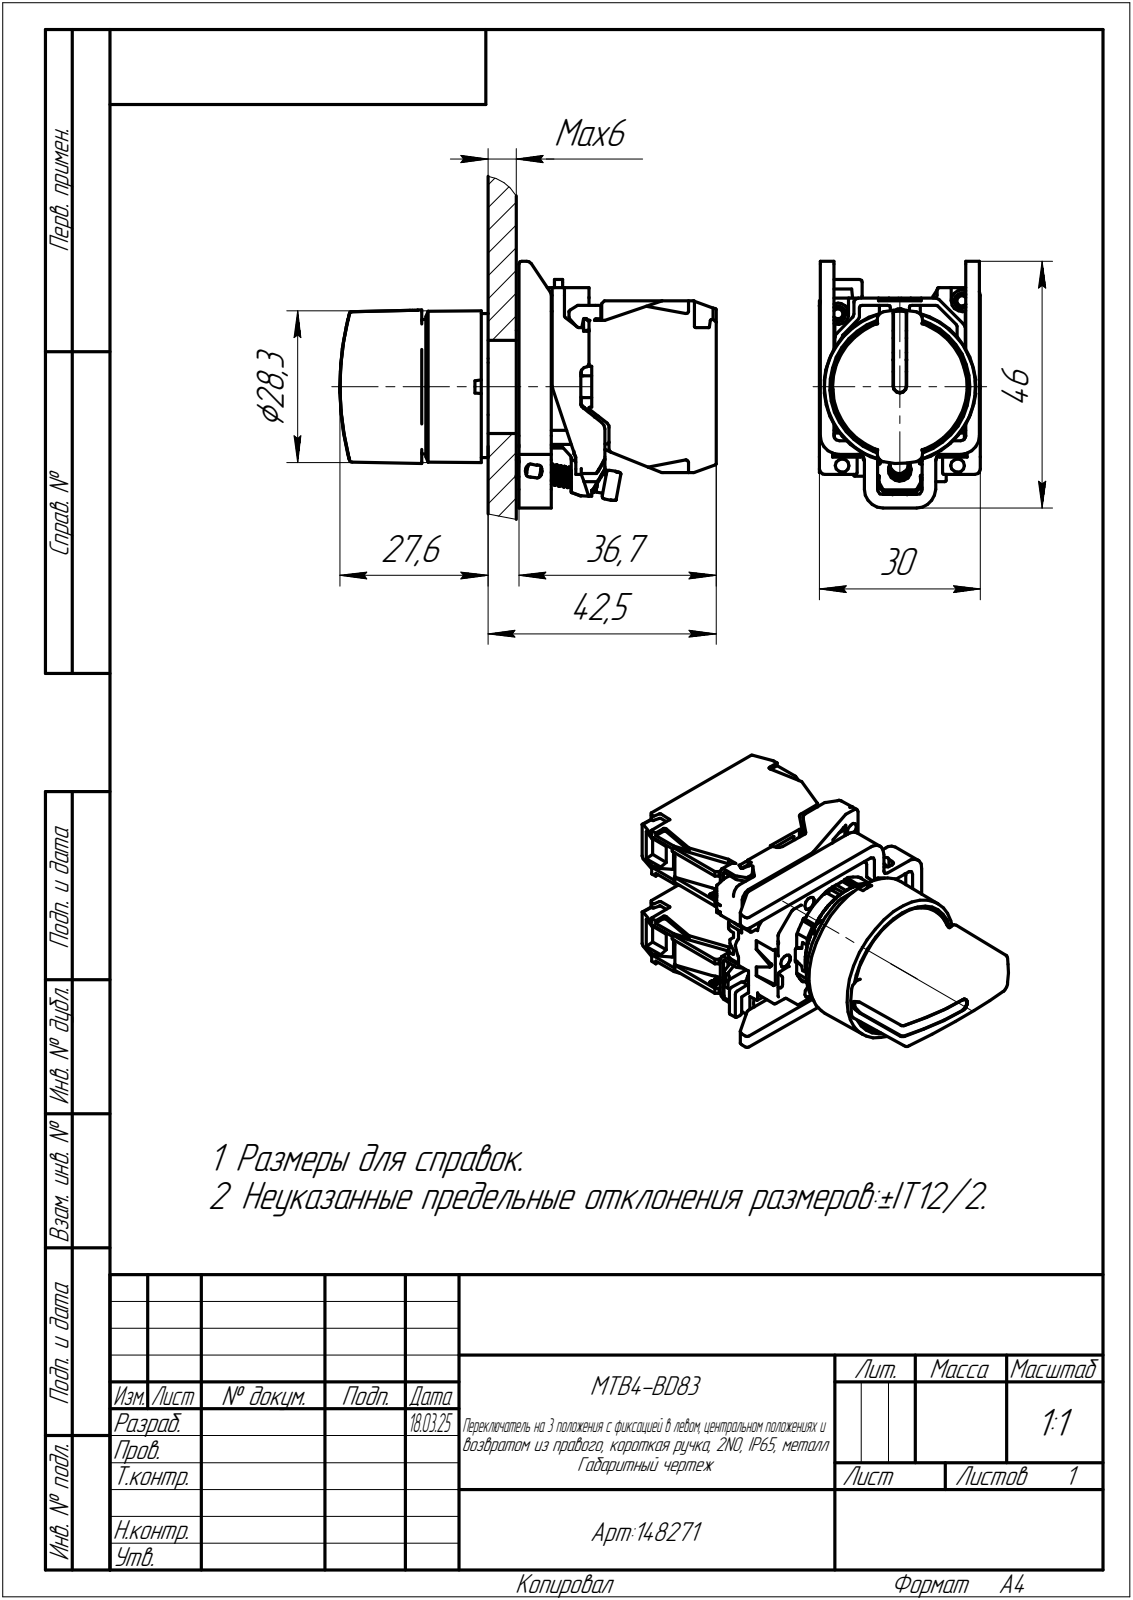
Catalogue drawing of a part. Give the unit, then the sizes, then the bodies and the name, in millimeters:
Units: millimetres
Overall size (bounding box): 70.1 × 46 × 30
Round holes (diameter × count): ⌀2.5 ×12, ⌀1.2 ×7, ⌀1.9 ×4, ⌀2.6 ×4, ⌀2.9 ×4, ⌀4 ×4, ⌀1 ×2, ⌀1.5 ×1, ⌀3 ×1, ⌀18.6 ×1
Round bosses / shafts (diameter × count): ⌀5.6 ×4, ⌀2.9 ×4, ⌀2.7 ×4, ⌀2.4 ×4, ⌀25 ×1, ⌀21 ×1, ⌀18.01 ×1, ⌀3.8 ×1
Partial cylindrical surfaces — rounded edges, fillets, slot ends (radius × count): R0.2 ×246, R0.1 ×134, R0.3 ×73, R0.15 ×62, R0.5 ×60, R1 ×42, R0.4 ×18, R2 ×15
Main face-to-face distances: 20, 9.8, 2.5, 29.8, 13.55, 1, 7, 6, 1.3, 6.4
Hole centre spacings: 4, 20, 4.5, 5.9, 6.09, 7.29, 7.45, 8.7
Volume: 30 504 mm³ · Surface area: 25 718 mm²
Bodies: 25 solids, 5387 faces (3338 planar, 1402 cylindrical, 647 other)
Part name (STEP PRODUCT): MTB4-BD83; ZB4BE009; ZBE101; ZB4BD3C
STEP written by: C3D Toolkit (CONFIG_CONTROL_DESIGN)
